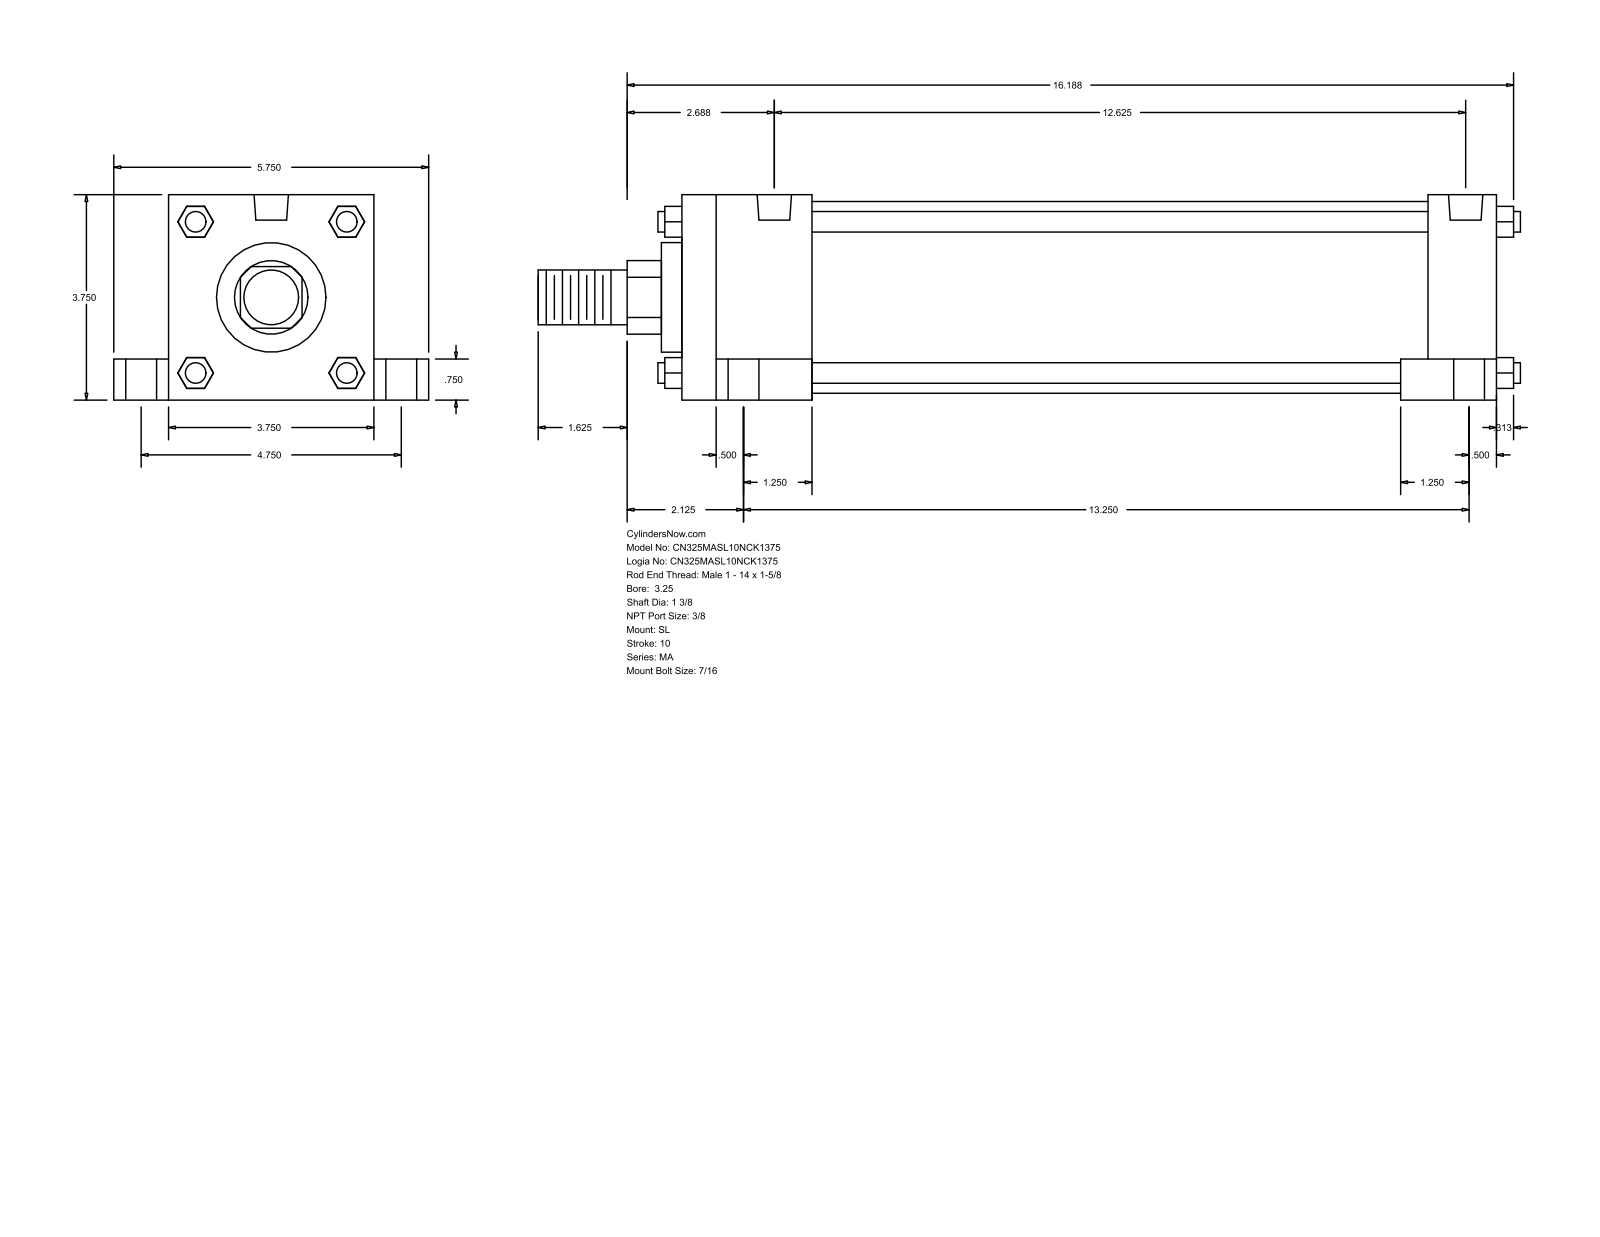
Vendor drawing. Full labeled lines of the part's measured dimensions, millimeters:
Part name (STEP PRODUCT): MA_SL__0325_1.375
STEP written by: GSSL Pune (CONFIG_CONTROL_DESIGN)
Units: millimetres
Bodies: 0 solids, 148 faces (112 planar, 36 cylindrical, 0 other)
Overall size (bounding box): 455.61 × 146.05 × 95.25
Round holes (diameter × count): ⌀11.11 ×4, ⌀14.29 ×4, ⌀20.64 ×4, ⌀15.93 ×2
Round bosses / shafts (diameter × count): ⌀9.53 ×4, ⌀88.9 ×1, ⌀50.8 ×1, ⌀34.92 ×1, ⌀25.4 ×1
Partial cylindrical surfaces — rounded edges, fillets, slot ends (radius × count): R17.06 ×1
Main face-to-face distances: 95.24, 377.83, 25.41, 120.65, 346.08, 31.75, 60.32, 285.76, 317.51, 19.05
Hole centre spacings: 60.35, 60.66, 62, 63.27, 120.66, 311.15, 323.17, 327.86
